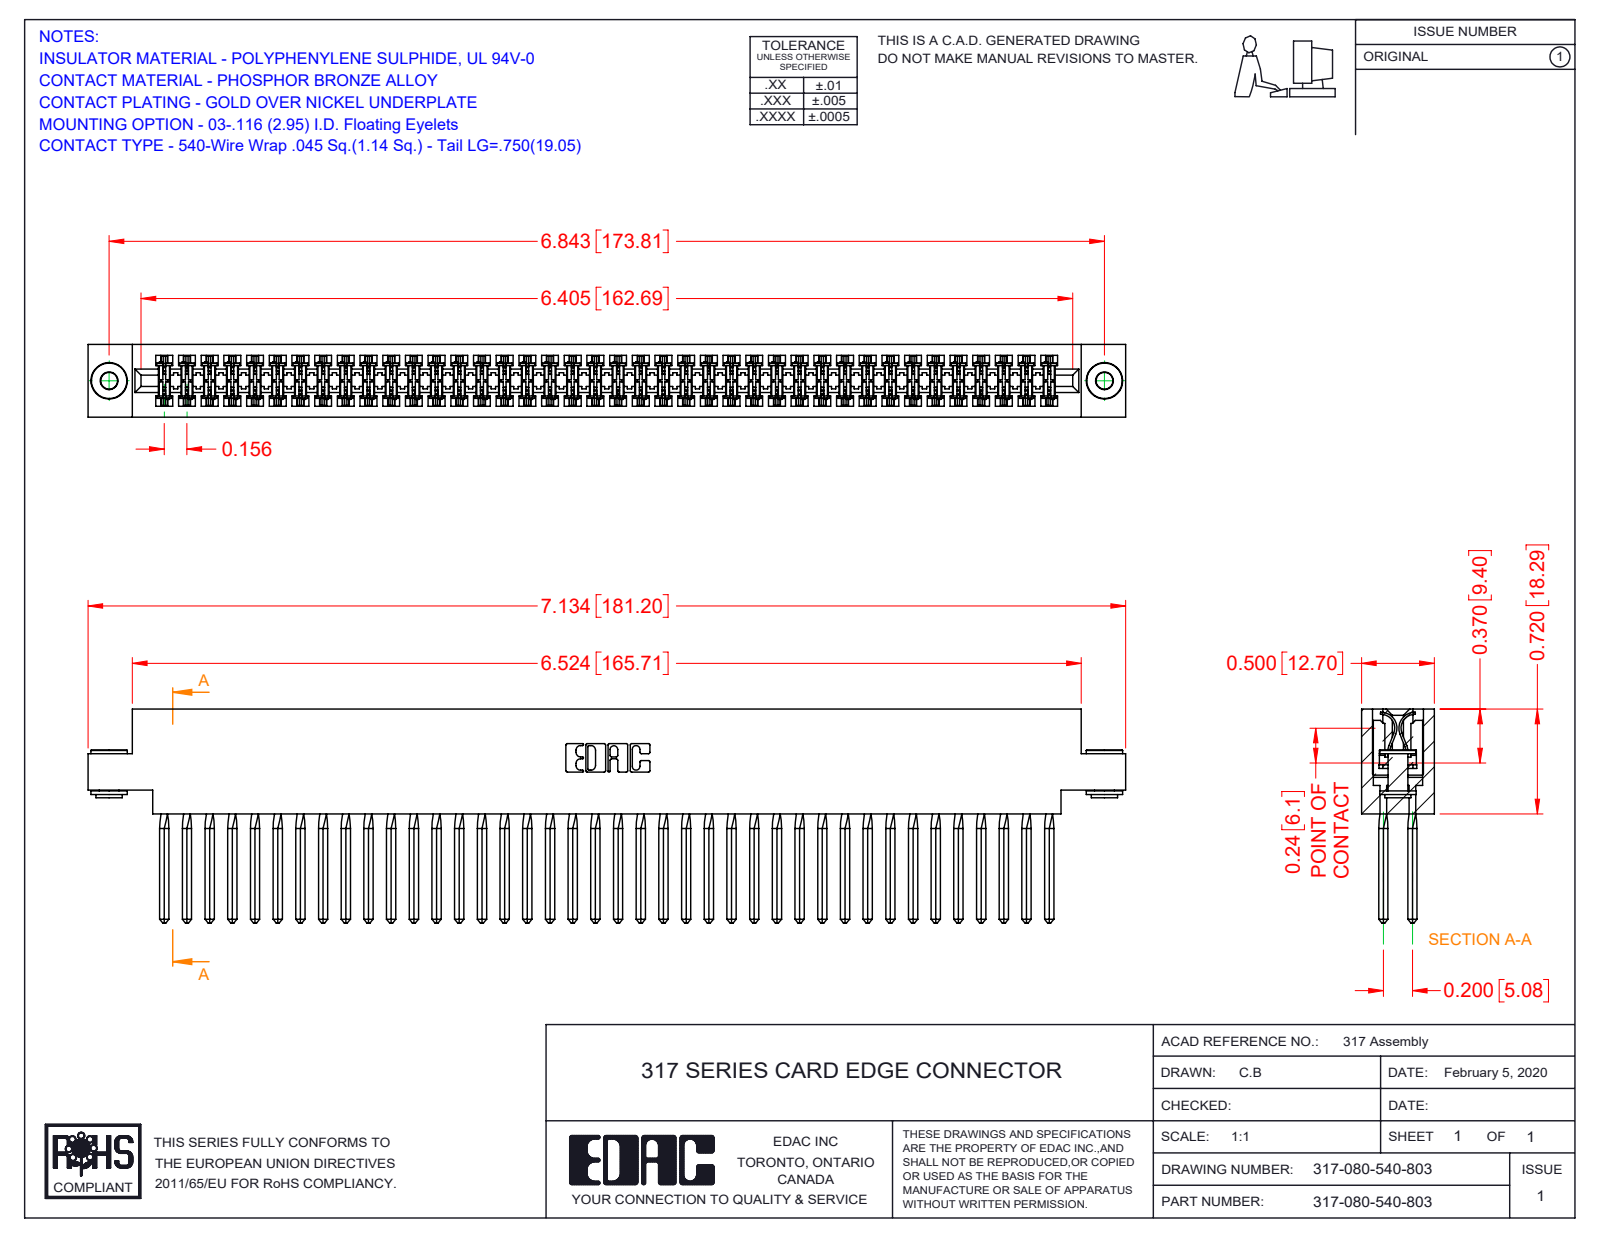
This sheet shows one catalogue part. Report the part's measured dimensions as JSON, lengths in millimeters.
{"part_name": "317-080-540-803; 317-290-001_540; 345-250-002_345-250-002-102; 317 Part_.156 Dia - TH", "step_written_by": "SolidWorks 2016 (CONFIG_CONTROL_DESIGN)", "units": "millimeters", "bodies": {"solids": 83, "faces": 7260, "planar": 5908, "cylindrical": 1024, "other": 328}, "overall_size": [181.2, 37.3, 12.7], "volume_mm3": 30370, "surface_area_mm2": 45410, "round_holes": [[2.9, 2], [4, 2]], "round_bosses_or_shafts": [[6.4, 2], [4.6, 2], [3.5, 2]], "partial_cylinders_radius": [[0.4, 160], [0.3, 22], [0.2, 6], [0.8, 6], [0.7, 3], [2.4, 2], [2.5, 2], [2.8, 2]], "face_to_face_distances": [12.7, 1.9, 10.8, 8.9, 5, 2.4, 5.1, 2.9, 3.3, 2.8], "hole_center_spacings": [173.8]}
